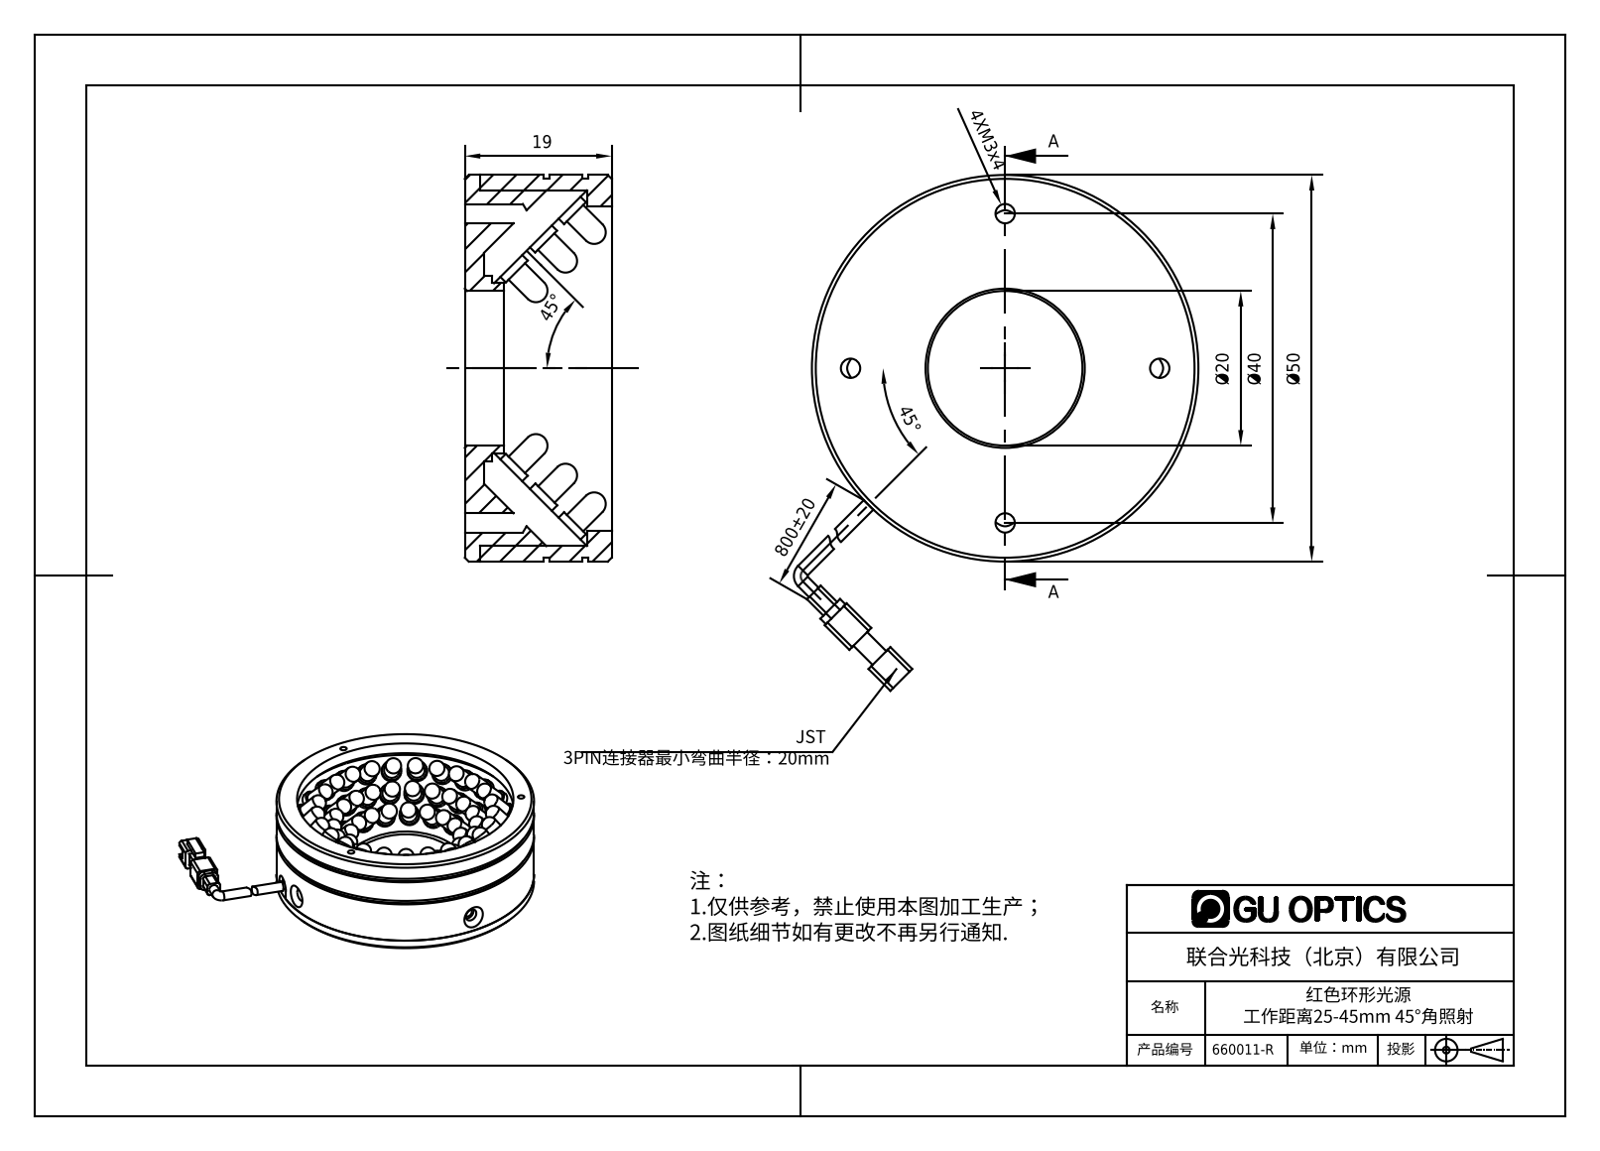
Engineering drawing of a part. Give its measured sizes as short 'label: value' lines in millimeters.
name: 660011-R
written by: SolidWorks 2016 (AUTOMOTIVE_DESIGN)
unit: mm
bodies: 70 solids, 1331 faces (857 planar, 361 cylindrical, 113 other)
size: 66.72 × 52.33 × 19
volume: 17 436 mm³; area: 21 875 mm²
holes: 4× ⌀2.5, 3× ⌀1.25, 3× ⌀3, 2× ⌀1.6, 2× ⌀2.4, 1× ⌀20, 1× ⌀42
bosses: 65× ⌀3.8, 63× ⌀3, 2× ⌀1.75, 1× ⌀50, 1× ⌀49, 1× ⌀46, 1× ⌀24, 1× ⌀22
rounds: 10× R0.5, 4× R1, 1× R1.6, 1× R4.5
face distances: 2, 0.5, 19, 17, 2.5, 1, 3, 16.5, 5, 0.8
hole spacings: 20, 28.28, 22.5, 38.97, 11.26, 30.1, 40, 2.5
